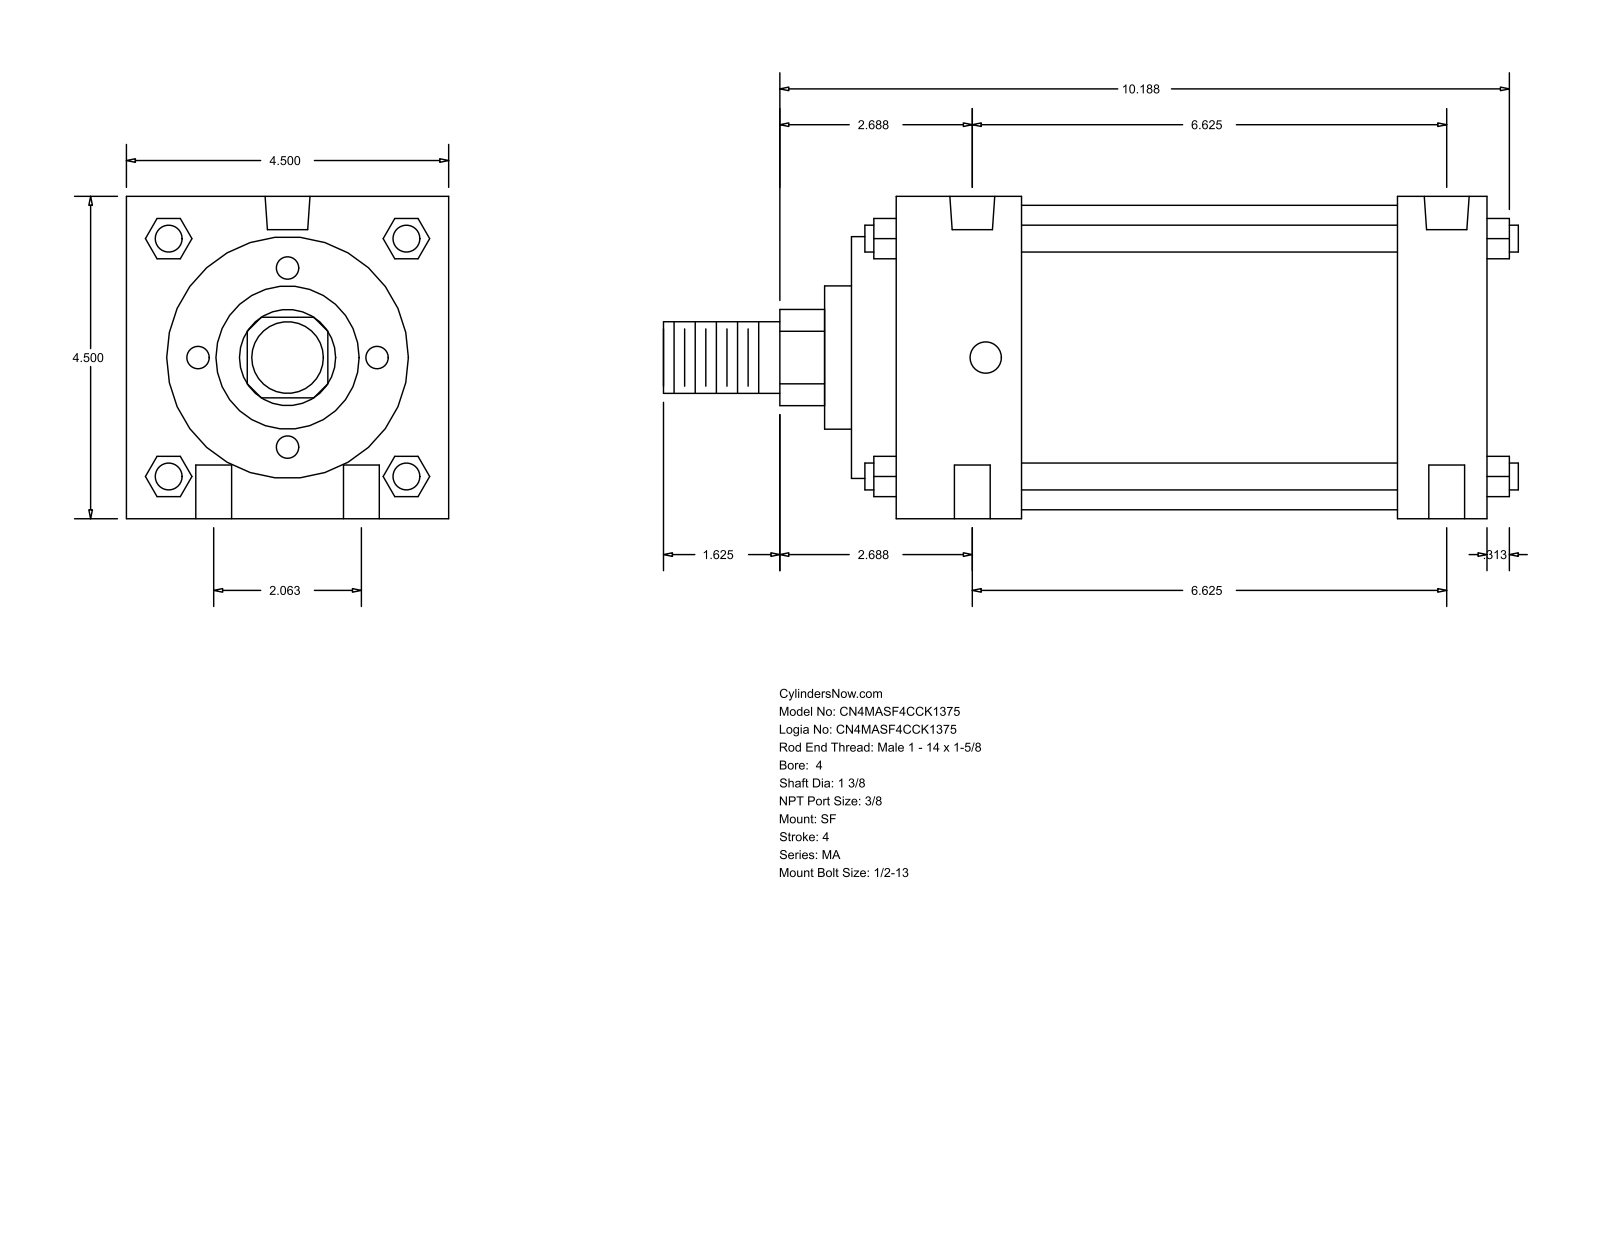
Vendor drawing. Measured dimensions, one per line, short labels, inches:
name: MA_SF__0400_1.375
written by: GSSL Pune (CONFIG_CONTROL_DESIGN)
unit: in
bodies: 0 solids, 126 faces (95 planar, 31 cylindrical, 0 other)
size: 11.937 × 4.5 × 4.5
holes: 4× ⌀0.5, 2× ⌀0.437, 2× ⌀0.627
bosses: 4× ⌀0.375, 1× ⌀4.25, 1× ⌀3.375, 1× ⌀2, 1× ⌀1.375, 1× ⌀1
rounds: 1× R0.672
face distances: 4.5, 8.25, 8.875, 0.625, 7.625, 7, 1.25, 2.375, 1.75, 5.25
hole spacings: 1.031, 6.705, 6.625, 2.062, 6.939, 6.25
